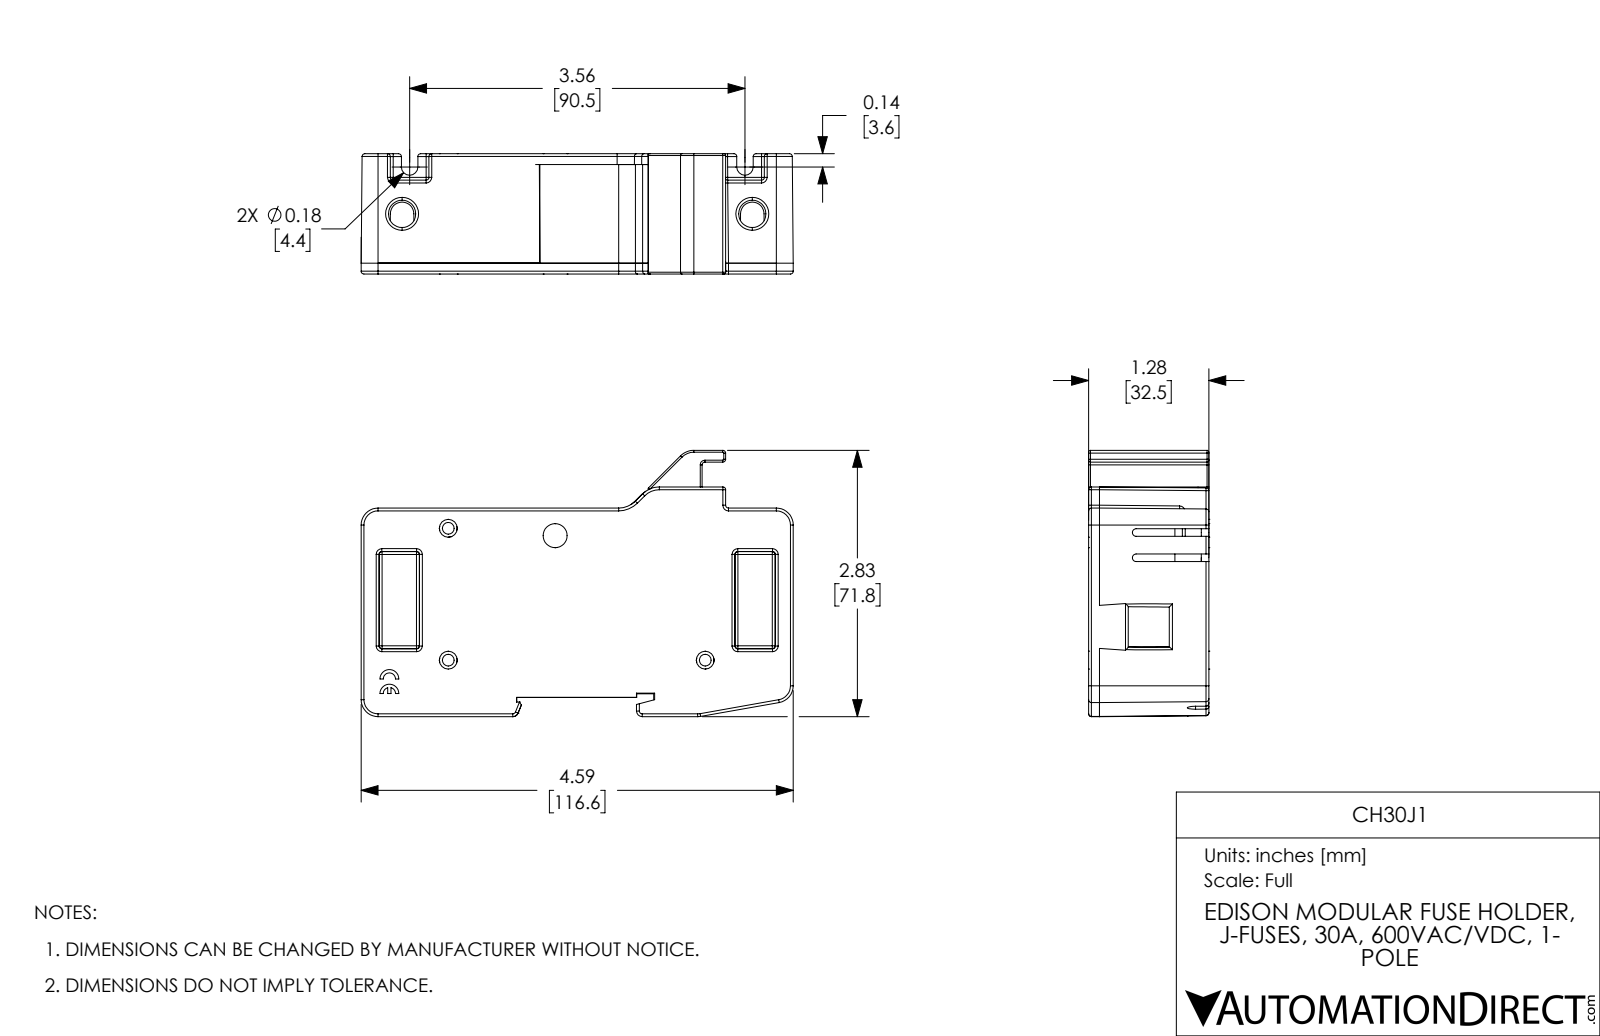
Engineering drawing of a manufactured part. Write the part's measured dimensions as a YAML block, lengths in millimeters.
part_name: "CH30J1"
step_written_by: "SolidWorks 2017 (AUTOMOTIVE_DESIGN)"
units: millimeters
bodies: {solids: 2, faces: 283, planar: 81, cylindrical: 143, other: 59}
overall_size: [116.6, 71.8, 32.5]
volume: 193000
surface_area: 33350
round_holes:
  - {diameter: 4.8, count: 3}
  - {diameter: 3.2, count: 2}
  - {diameter: 7.4, count: 2}
  - {diameter: 3.2, count: 1}
  - {diameter: 6.5, count: 1}
partial_cylinders:
  - {radius: 0.8, count: 41}
  - {radius: 0.8, count: 23}
  - {radius: 0.5, count: 10}
  - {radius: 1, count: 4}
  - {radius: 4.6, count: 3}
  - {radius: 2.2, count: 2}
  - {radius: 6.4, count: 2}
  - {radius: 0.3, count: 1}
face_to_face_distances: [32.5, 56.3, 116.6, 5.2, 51.1, 7.1, 25.3, 0.8, 55.5, 50.3]
hole_center_spacings: [28.9, 35.6, 44.2, 52.6, 69.3, 77.9, 94.5]
